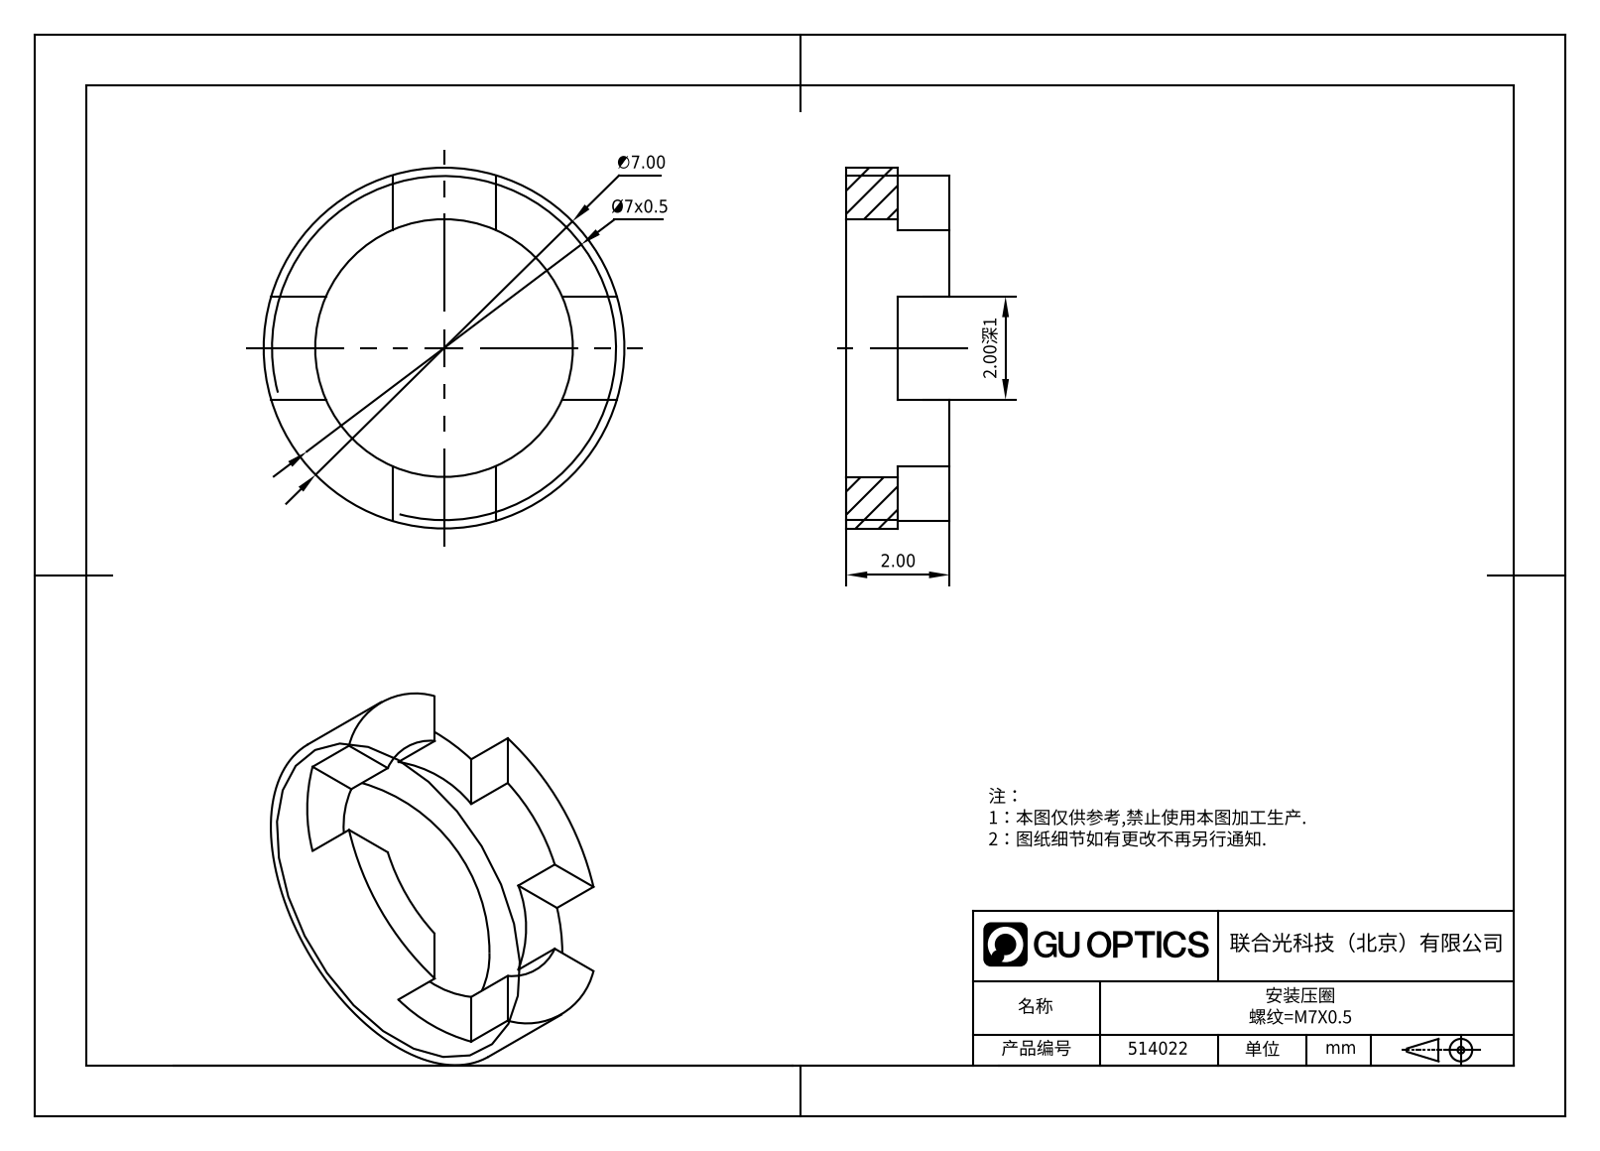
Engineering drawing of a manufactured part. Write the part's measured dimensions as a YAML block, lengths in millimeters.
part_name: "514022"
step_written_by: "SolidWorks 2020 (CONFIG_CONTROL_DESIGN)"
units: millimeters
bodies: {solids: 1, faces: 21, planar: 17, cylindrical: 4, other: 0}
overall_size: [7, 7, 2]
volume: 30
surface_area: 105
round_holes:
  - {diameter: 5, count: 1}
round_bosses_or_shafts:
  - {diameter: 7, count: 1}
face_to_face_distances: [1, 2]
